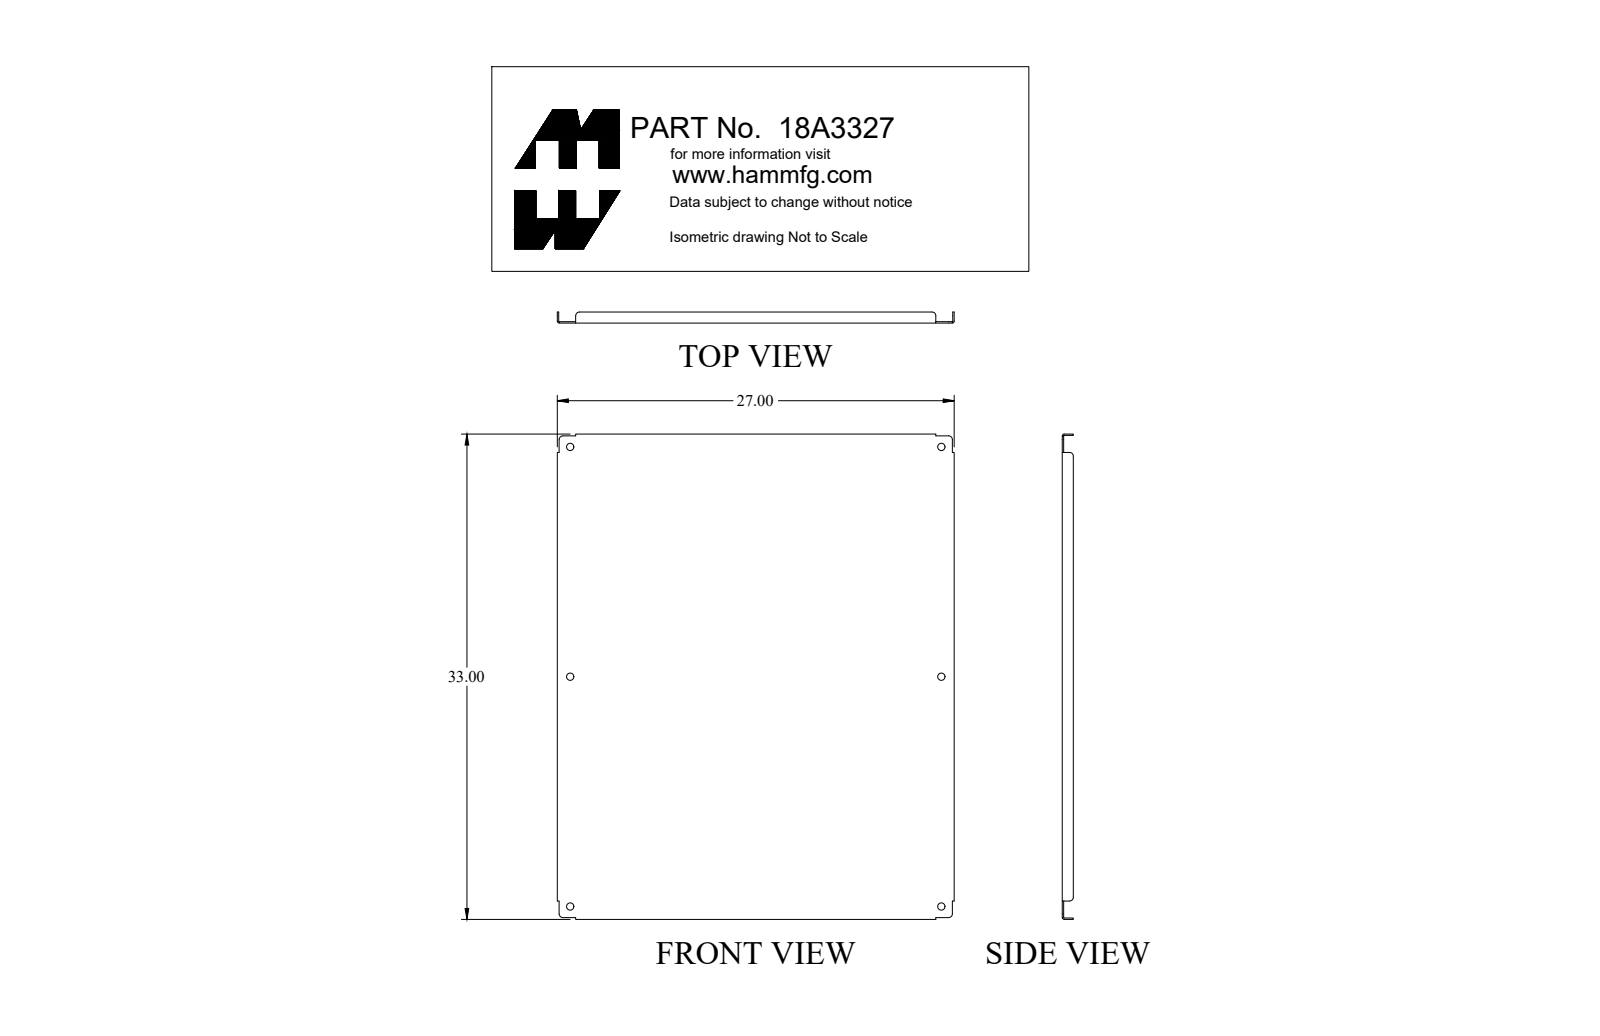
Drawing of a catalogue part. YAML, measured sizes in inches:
part_name: "18A3327"
step_written_by: "SolidWorks 2018 (AUTOMOTIVE_DESIGN)"
units: inches
bodies: {solids: 1, faces: 56, planar: 30, cylindrical: 26, other: 0}
overall_size: [33, 27, 0.75]
volume: 90.9
surface_area: 1926
round_holes:
  - {diameter: 0.5, count: 6}
partial_cylinders:
  - {radius: 0.25, count: 8}
  - {radius: 0.03, count: 4}
  - {radius: 0.125, count: 4}
face_to_face_distances: [0.095, 26.905, 32.905, 27, 26.81, 33, 32.81, 0.75, 0.655, 0.125]
hole_center_spacings: [15.625, 29.694, 25.25, 31.25, 40.177]
